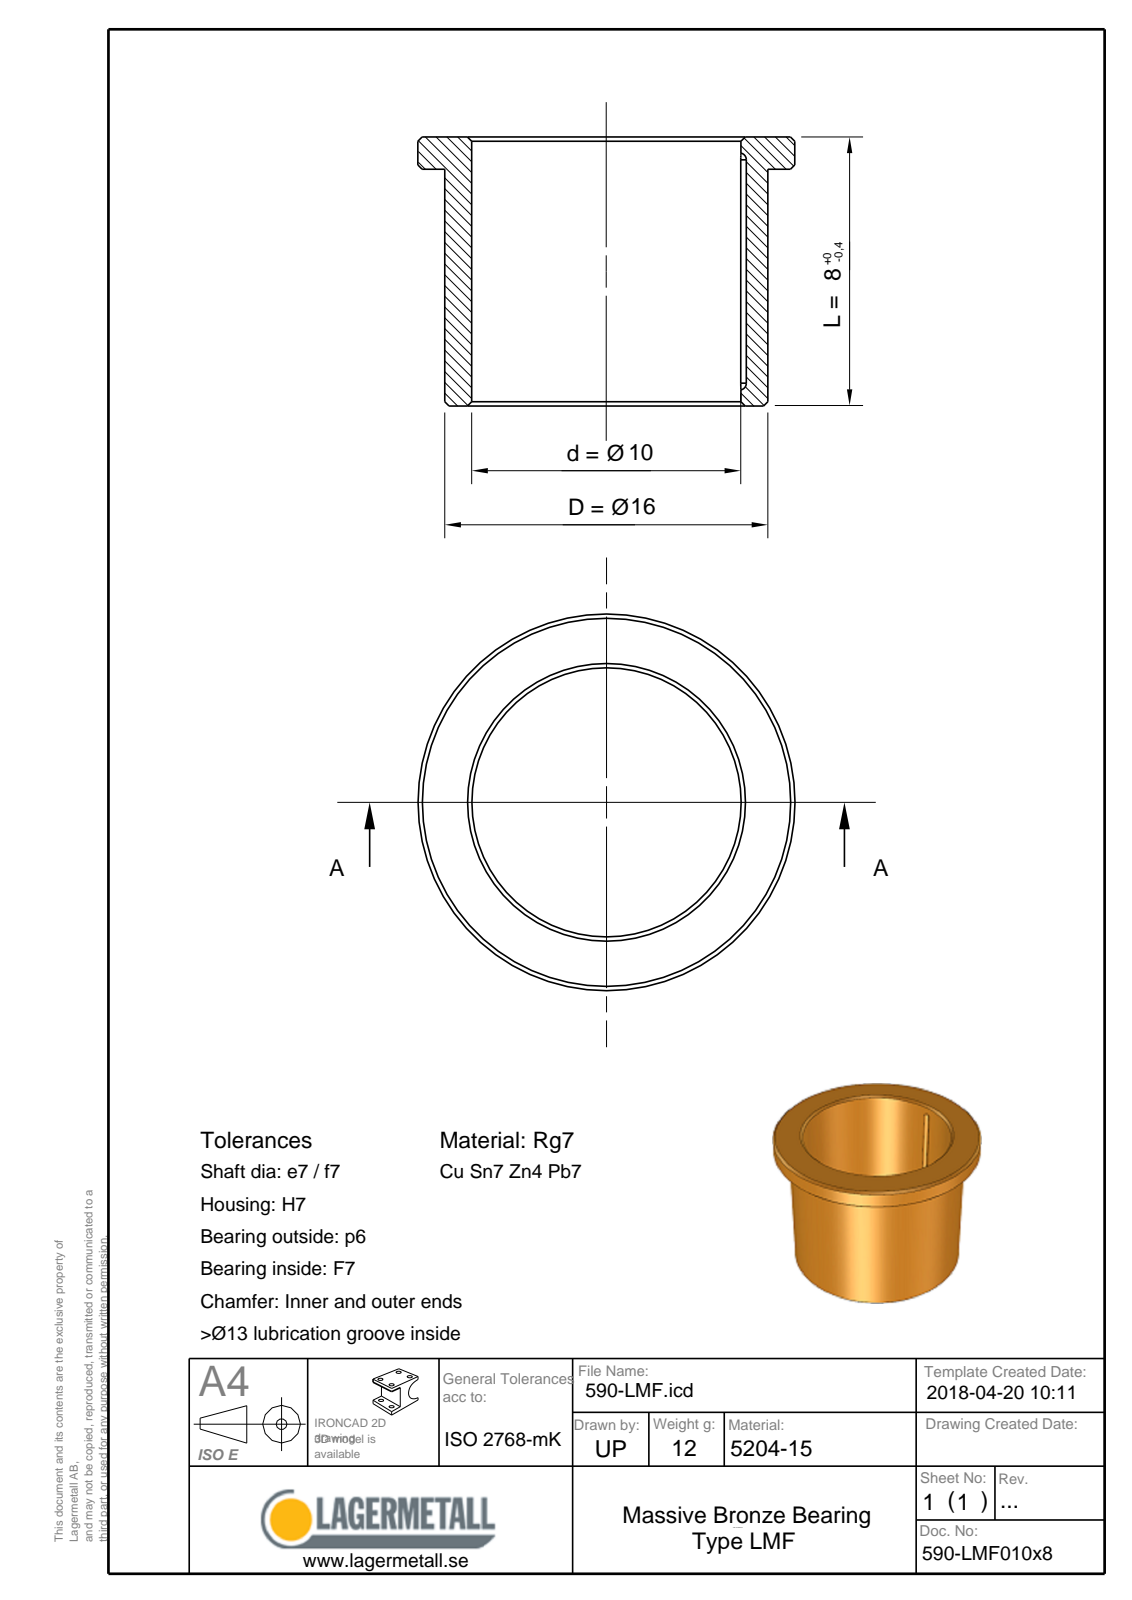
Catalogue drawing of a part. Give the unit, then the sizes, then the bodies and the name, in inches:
Units: inches
Overall size (bounding box): 0.787 × 0.787 × 0.315
Round holes (diameter × count): ⌀0.394 ×1
Round bosses / shafts (diameter × count): ⌀0.787 ×1, ⌀0.63 ×1
Main face-to-face distances: 0.315, 0.197, 0.118
Volume: 0.08 in³ · Surface area: 1.736 in²
Bodies: 1 solid, 11 faces (3 planar, 3 cylindrical, 5 other)
Part name (STEP PRODUCT): 590-LMF010x8
STEP written by: Spatial InterOp 3D (CONFIG_CONTROL_DESIGN)
